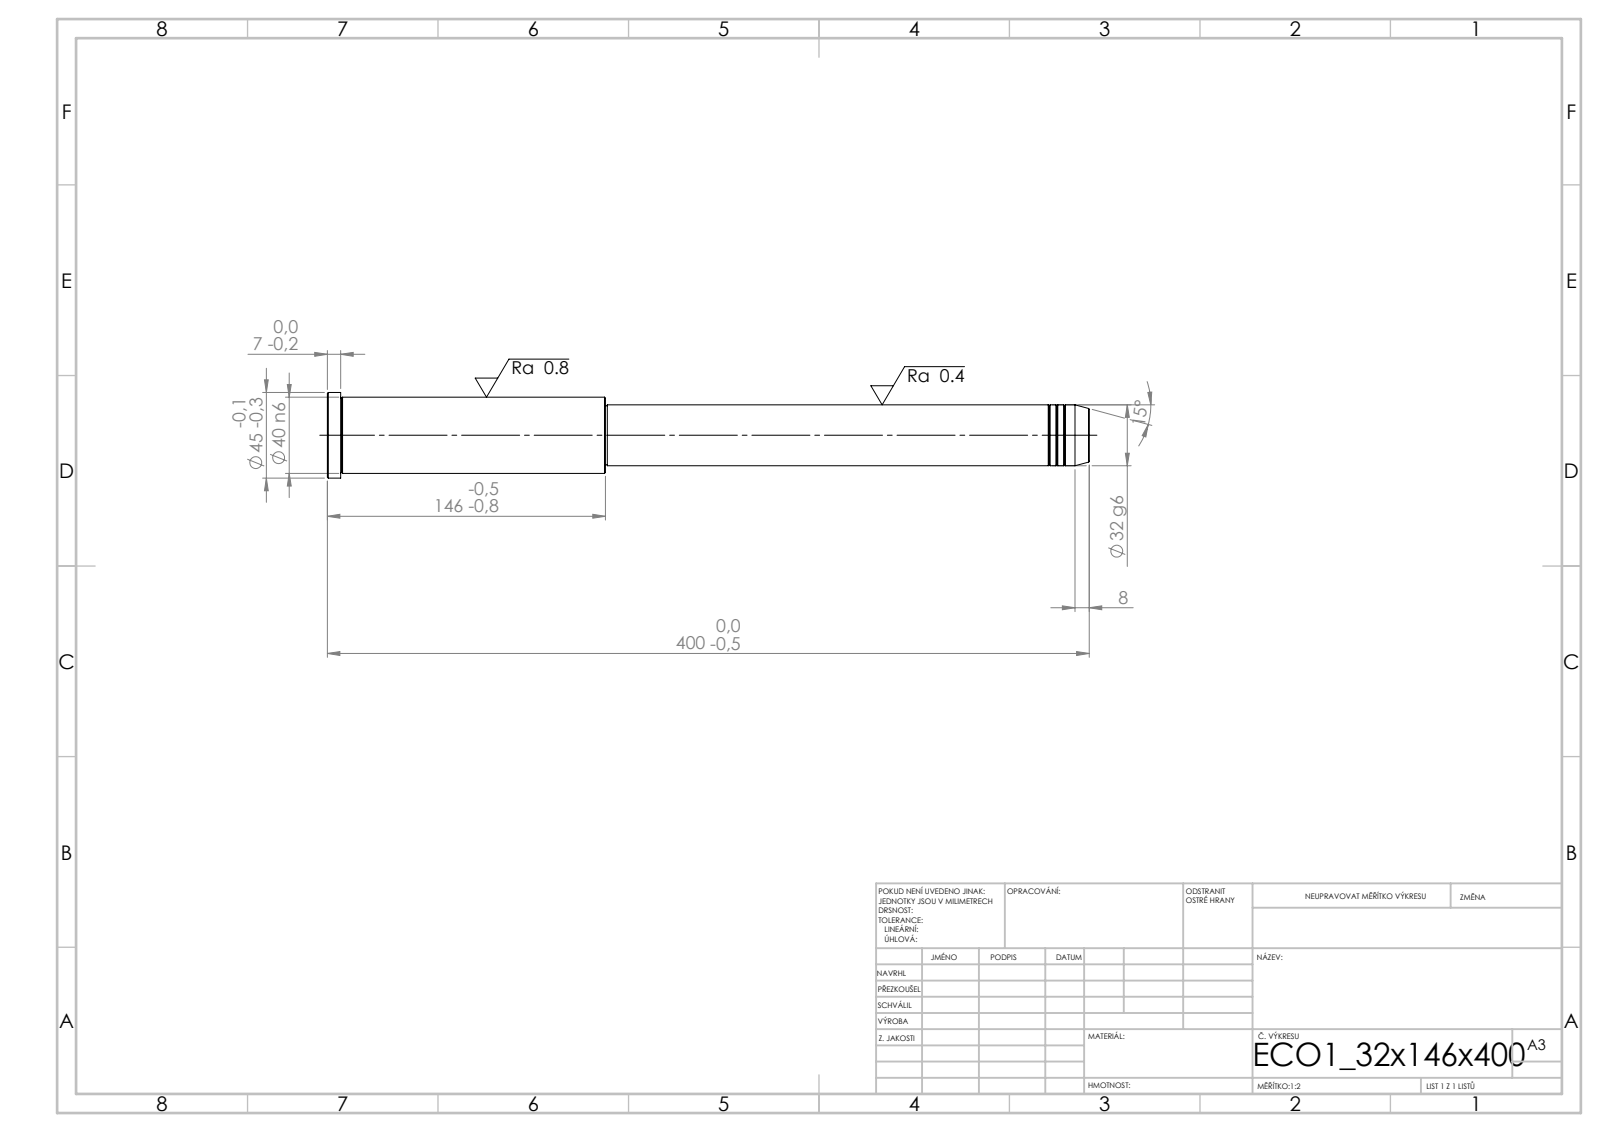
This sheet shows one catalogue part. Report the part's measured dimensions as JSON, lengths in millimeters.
{"step_written_by": "SolidWorks 2019 (CONFIG_CONTROL_DESIGN)", "units": "millimeters", "bodies": {"solids": 1, "faces": 43, "planar": 5, "cylindrical": 14, "other": 24}, "overall_size": [400, 45, 45], "volume_mm3": 389108, "surface_area_mm2": 47199, "round_bosses_or_shafts": [[45, 1], [40, 1], [32, 1], [31, 1]], "face_to_face_distances": [400, 254, 146, 393, 139, 7, 253, 1, 140, 147]}
